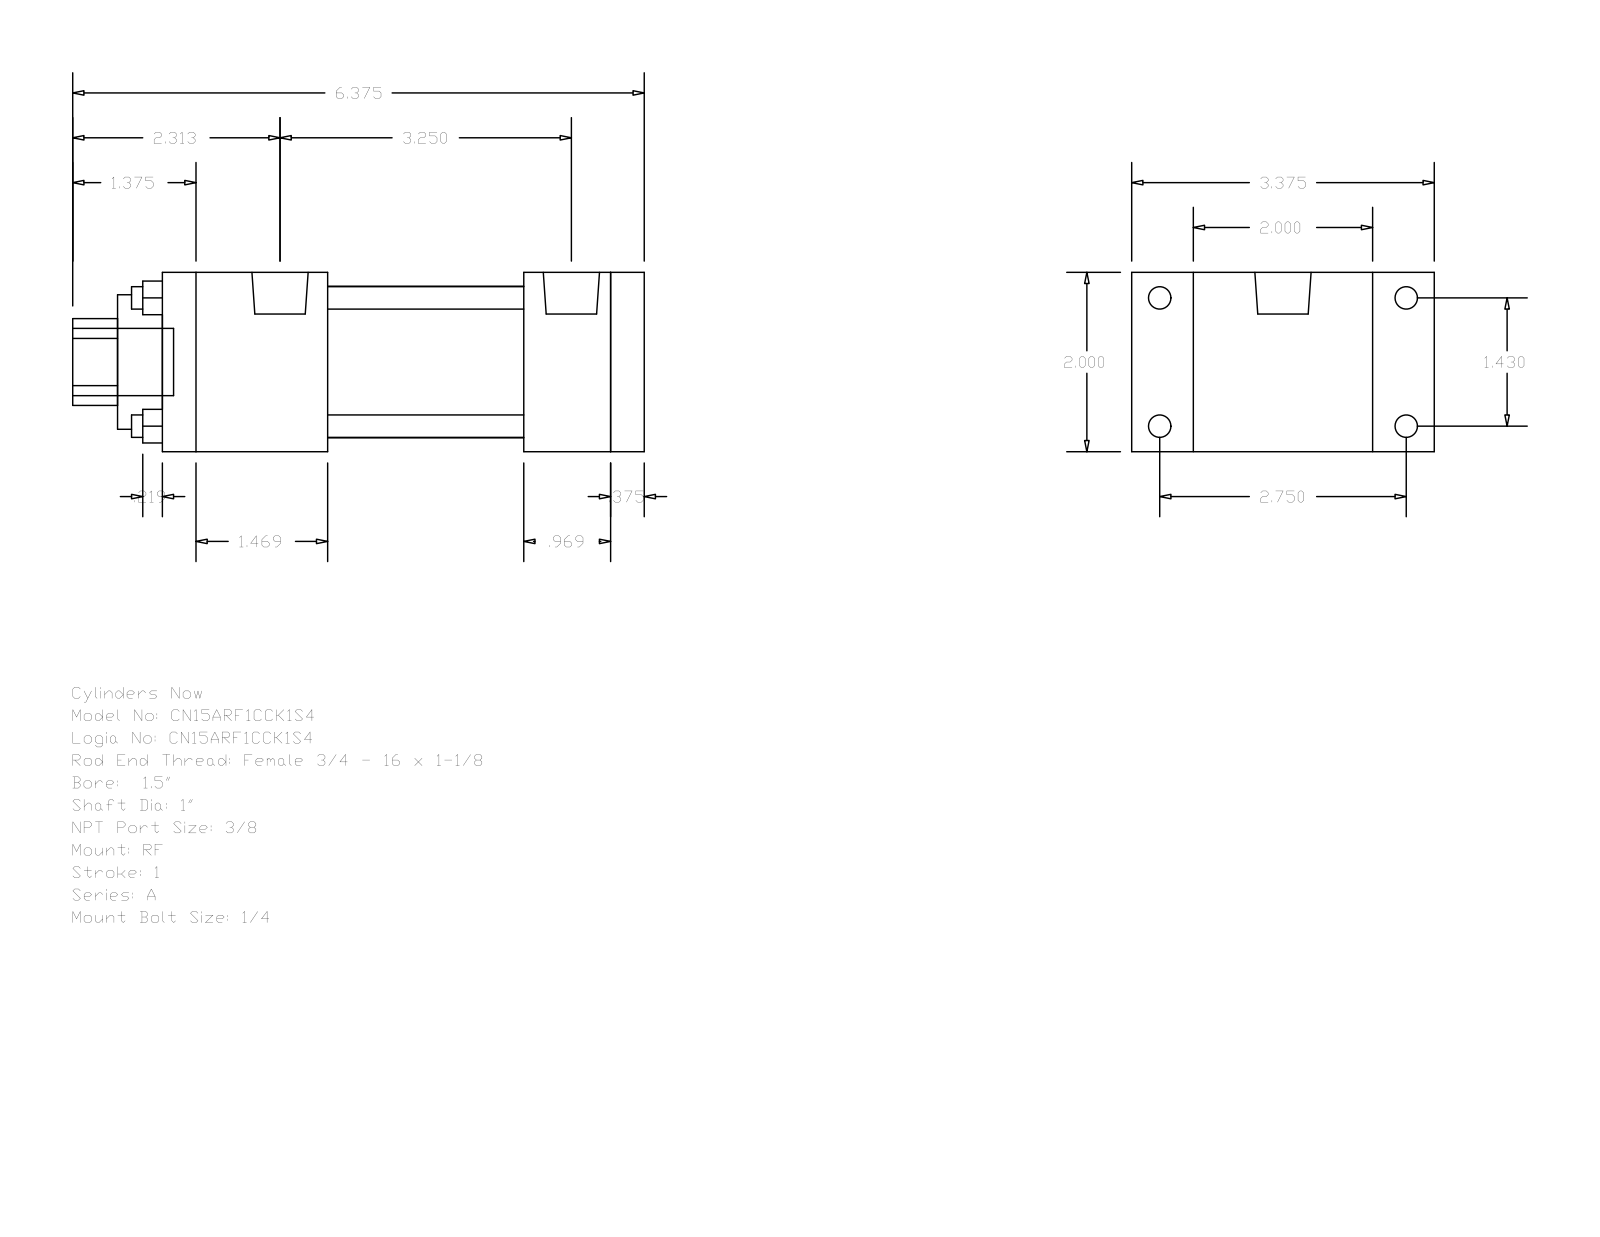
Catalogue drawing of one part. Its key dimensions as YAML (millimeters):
part_name: "A_RF__0150_1"
step_written_by: "GSSL Pune (CONFIG_CONTROL_DESIGN)"
units: millimeters
bodies: {solids: 0, faces: 92, planar: 64, cylindrical: 28, other: 0}
overall_size: [161.93, 85.72, 50.8]
round_holes:
  - {diameter: 6.35, count: 4}
  - {diameter: 25.4, count: 1}
  - {diameter: 38.1, count: 1}
  - {diameter: 42.93, count: 1}
round_bosses_or_shafts:
  - {diameter: 6.35, count: 4}
  - {diameter: 5.56, count: 4}
  - {diameter: 15.93, count: 2}
  - {diameter: 19.05, count: 1}
partial_cylinders:
  - {radius: 12.29, count: 1}
face_to_face_distances: [50.8, 9.53, 55.56, 127, 136.53, 102.39, 24.61, 34.14, 46.83, 80.17]
hole_center_spacings: [25.68, 36.32, 51.36]
